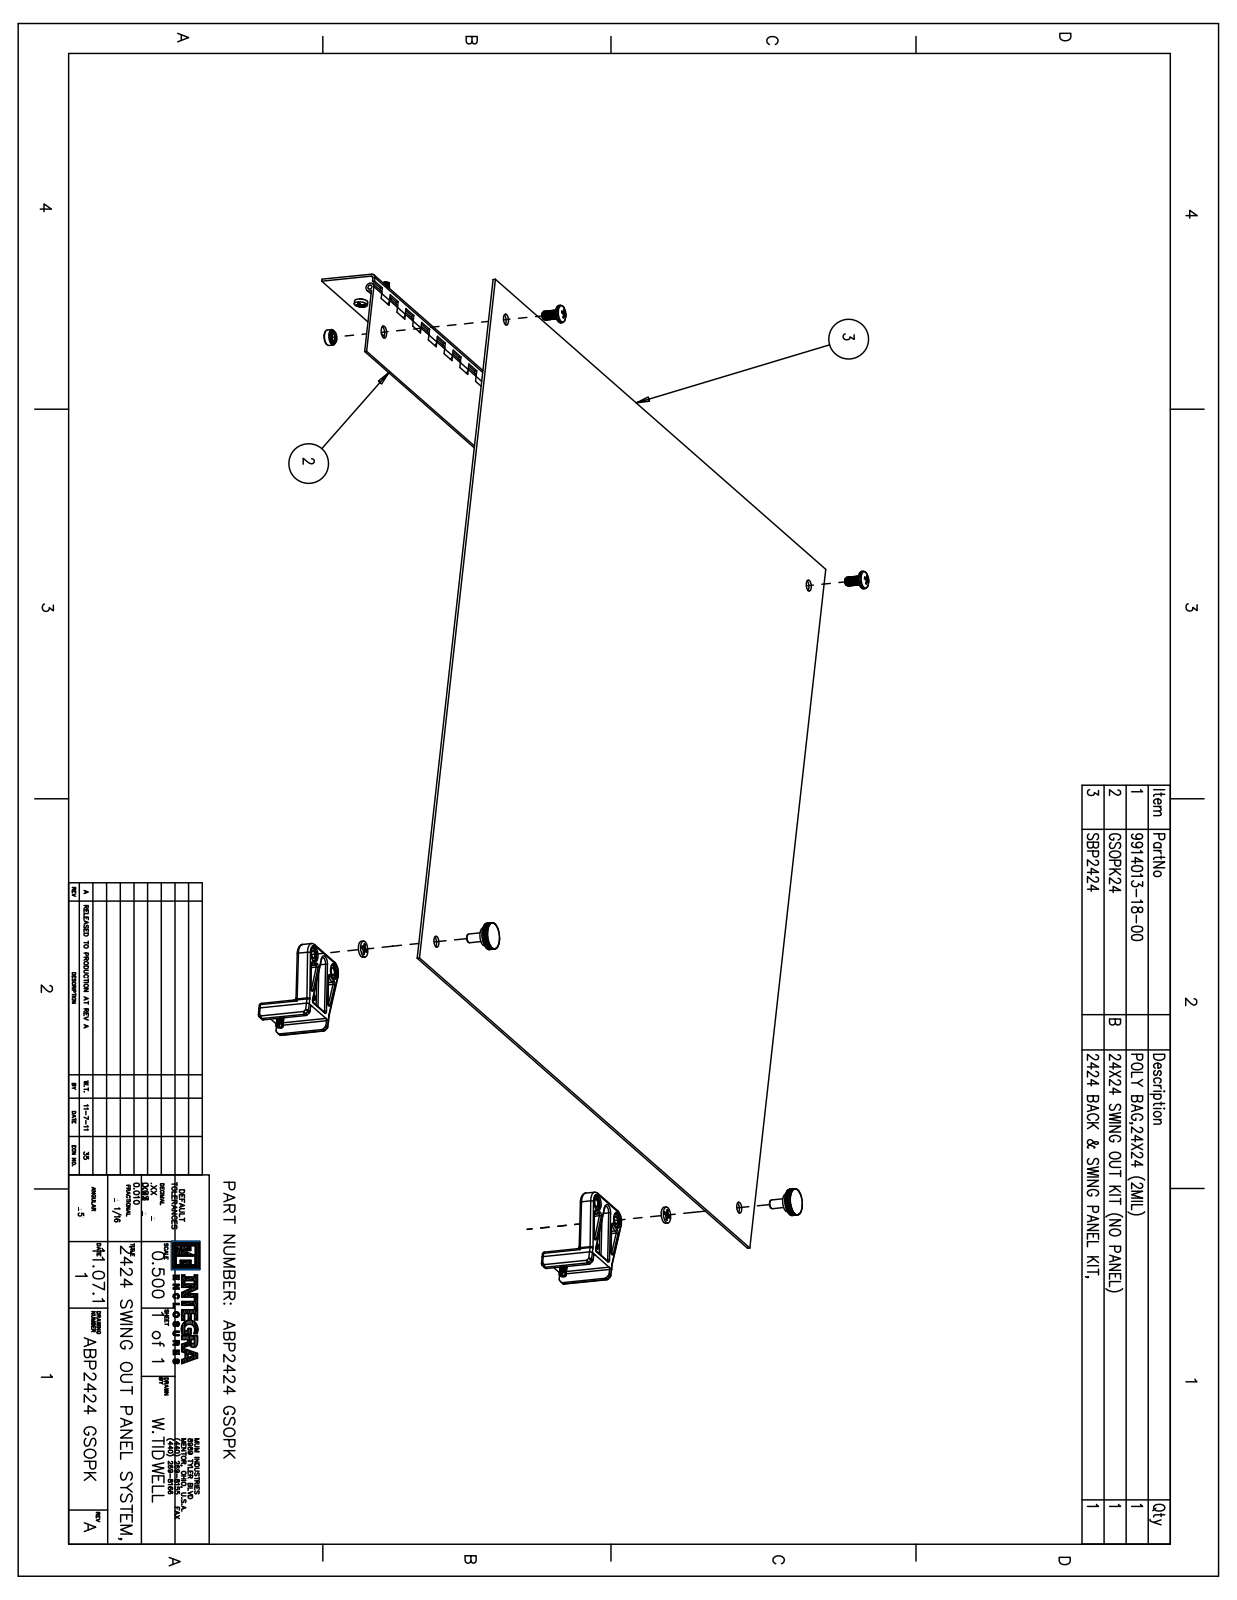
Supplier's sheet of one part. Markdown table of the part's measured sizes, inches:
| quantity | value |
| --- | --- |
| part name | ABP-2424GSOPK-P10 |
| STEP written by | SolidWorks 2018 (AUTOMOTIVE_DESIGN) |
| units | inches |
| bodies | 27 solids, 3050 faces (1870 planar, 630 cylindrical, 550 other) |
| overall size | 23.078 × 21 × 2.135 |
| volume | 44.05 in³ |
| surface area | 1 130 in² |
| round holes (diameter × count) | 0.212 × 8, 0.25 × 6, 0.312 × 6, 0.203 × 4, 0.443 × 4, 0.206 × 2, 0.269 × 2, 0.31 × 2, 0.313 × 2, 0.125 × 1, 0.125 × 1 |
| round bosses / shafts (diameter × count) | 0.375 × 10, 0.19 × 6, 0.16 × 6, 0.25 × 5, 0.492 × 4, 0.35 × 4, 0.185 × 4, 0.507 × 2 |
| partial cylindrical surfaces (radius × count) | 0.01 × 180, 0.06 × 53, 0.04 × 34, 0.05 × 4, 0.106 × 4, 0.125 × 4, 0.31 × 4, 0.086 × 2 |
| main face-to-face distances | 0.08, 0.063, 0.143, 21, 0.65, 21.65, 0.16, 22.3, 22.237, 22.14 |
| hole center spacings | 19.25, 27.223, 1.25, 18, 19.25, 0.02, 18, 18.877 |
